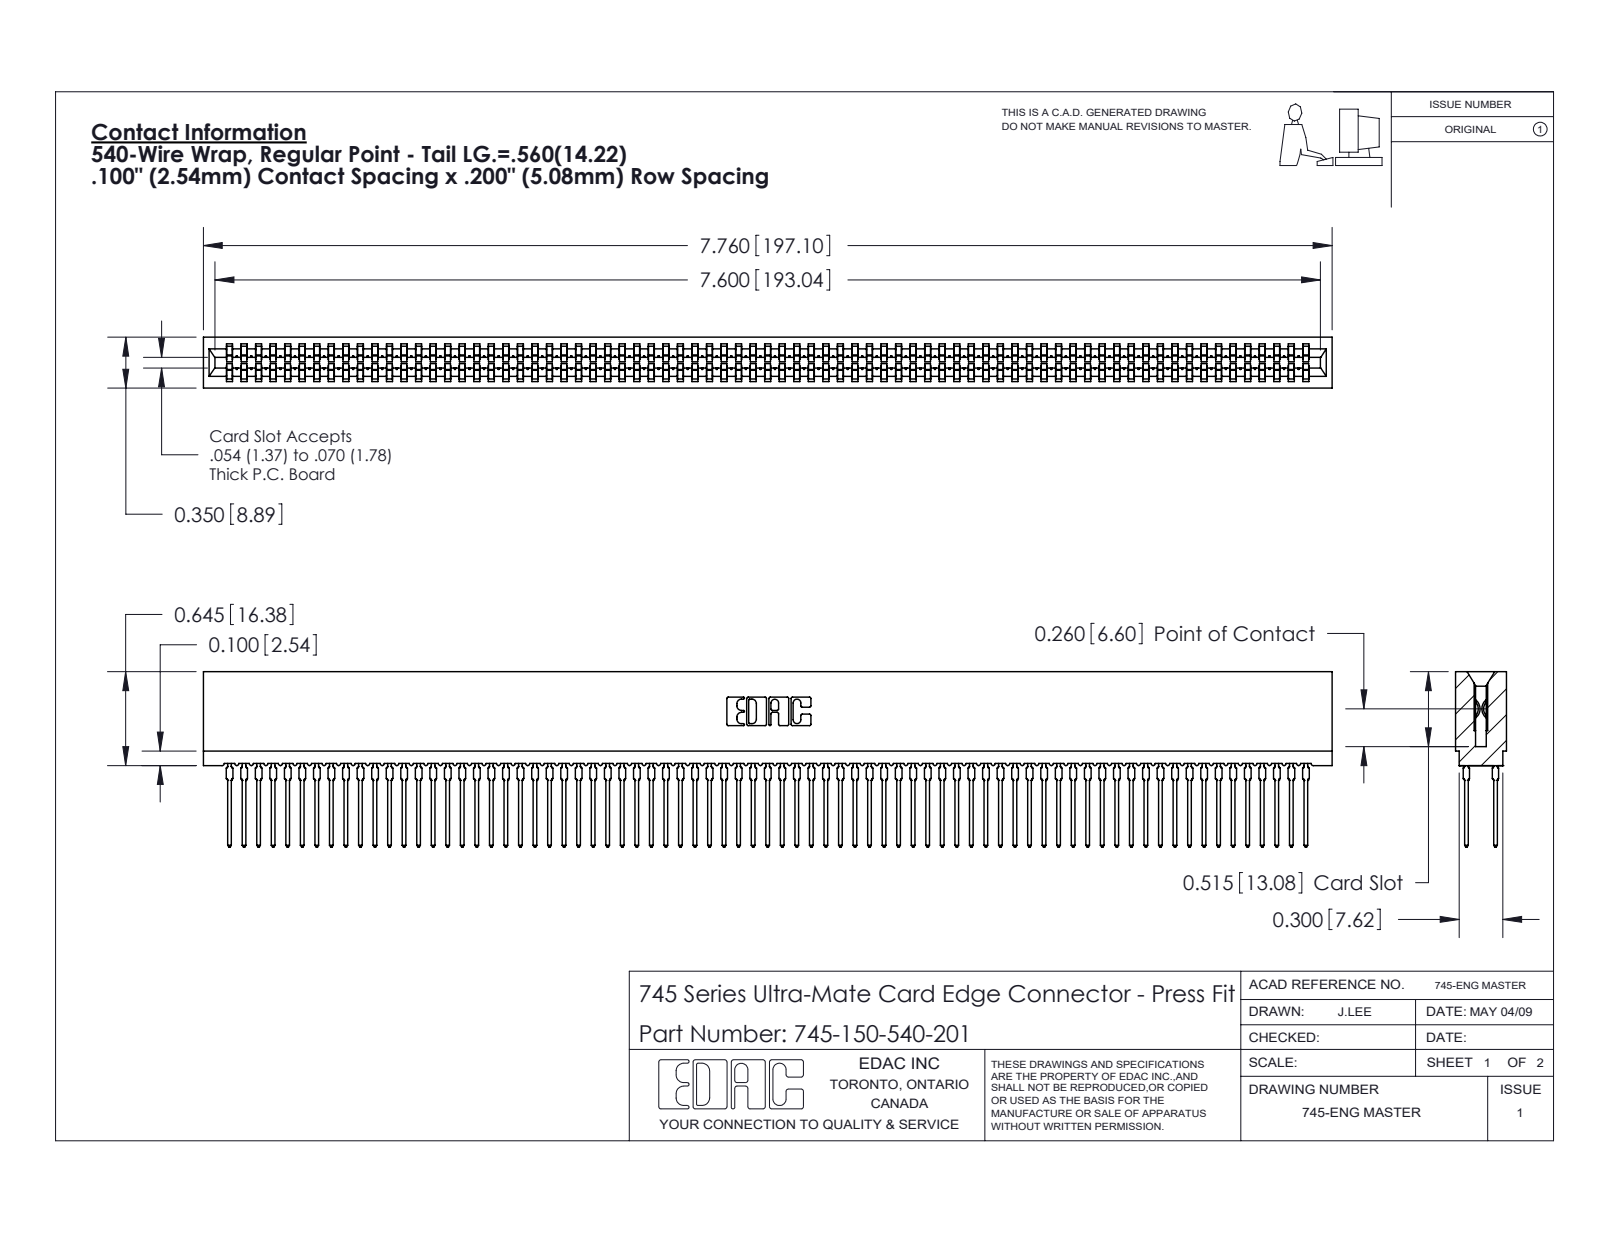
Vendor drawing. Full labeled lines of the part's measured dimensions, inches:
Part name (STEP PRODUCT): 745-292-001_540; 745 Part_Insulator Option - 01; 745-150-540-201
STEP written by: SolidWorks 2020 (CONFIG_CONTROL_DESIGN)
Units: inches
Bodies: 151 solids, 13520 faces (6955 planar, 2665 cylindrical, 3900 other)
Overall size (bounding box): 7.76 × 1.206 × 0.35
Volume: 1.098 in³ · Surface area: 60.57 in²
Partial cylindrical surfaces — rounded edges, fillets, slot ends (radius × count): R0.021 ×300, R0.015 ×150, R0.01 ×22, R0.005 ×8, R0.011 ×8, R0.007 ×6, R0.031 ×6, R0.026 ×3
Main face-to-face distances: 0.063, 0.287, 0.35, 0.2, 0.045, 0.305, 0.018, 0.243, 0.138, 0.212
